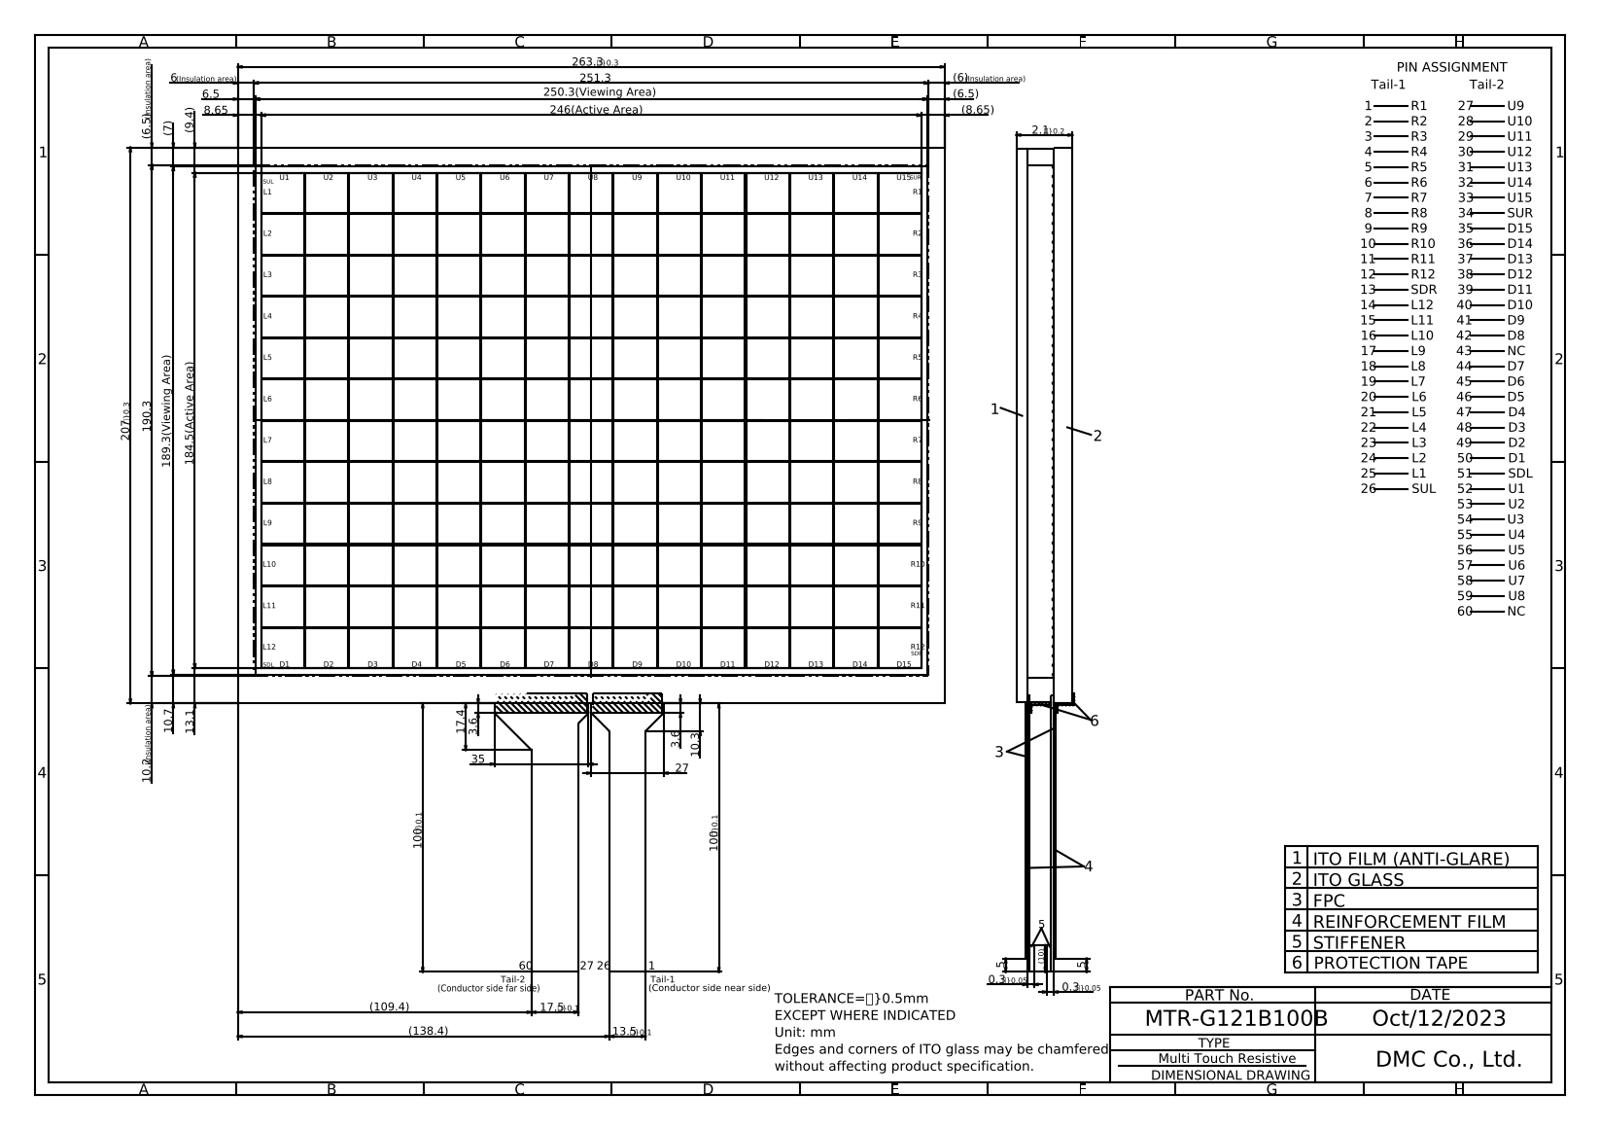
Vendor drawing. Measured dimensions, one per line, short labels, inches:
name: MTR-G121B100B
written by: Autodesk Inventor 2020 (CONFIG_CONTROL_DESIGN)
unit: in
bodies: 1 solid, 294 faces (282 planar, 12 cylindrical, 0 other)
size: 14.513 × 13.717 × 0.087
volume: 6.998 in³; area: 182.8 in²
rounds: 8× R0.039, 4× R0.008
face distances: 0.083, 0.071, 0.075, 0.079, 8.15, 10.366, 0.016, 0.087, 0.02, 0.028
